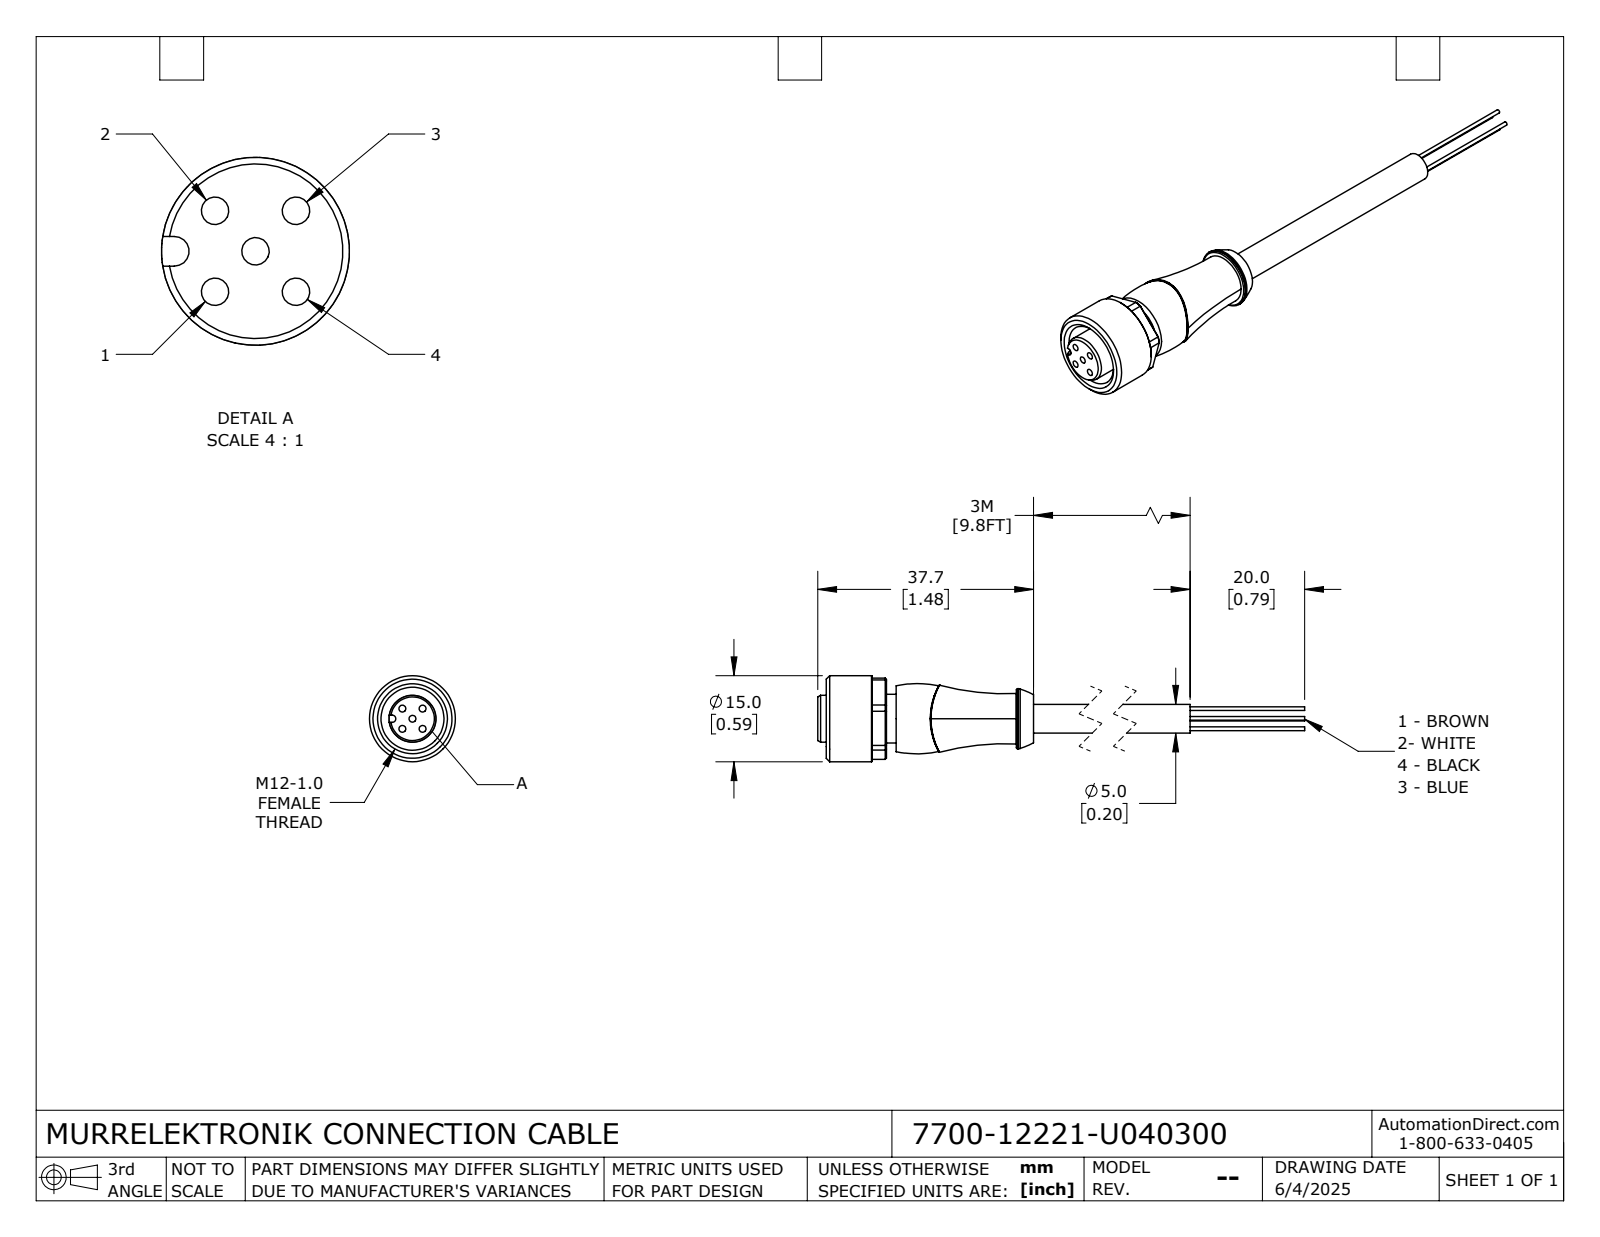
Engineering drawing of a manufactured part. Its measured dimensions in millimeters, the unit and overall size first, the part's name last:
Units: millimetres
Overall size (bounding box): 102.7 × 15 × 15
Round holes (diameter × count): ⌀1.2 ×5, ⌀11 ×1
Round bosses / shafts (diameter × count): ⌀0.64 ×4, ⌀15 ×1, ⌀10.5 ×1, ⌀8.5 ×1, ⌀8.2 ×1, ⌀5 ×1
Partial cylindrical surfaces — rounded edges, fillets, slot ends (radius × count): R0.65 ×1, R7.2 ×1
Main face-to-face distances: 3, 25.7, 1.7, 13, 4.7, 9, 12, 13.7, 37.7, 28.7
Hole centre spacings: 2.5, 3.53, 3.54, 5
Volume: 4 577 mm³ · Surface area: 3 233 mm²
Bodies: 1 solid, 110 faces (36 planar, 39 cylindrical, 35 other)
Part name (STEP PRODUCT): 7700-12221-U040300
STEP written by: SolidWorks 2024 (CONFIG_CONTROL_DESIGN)
